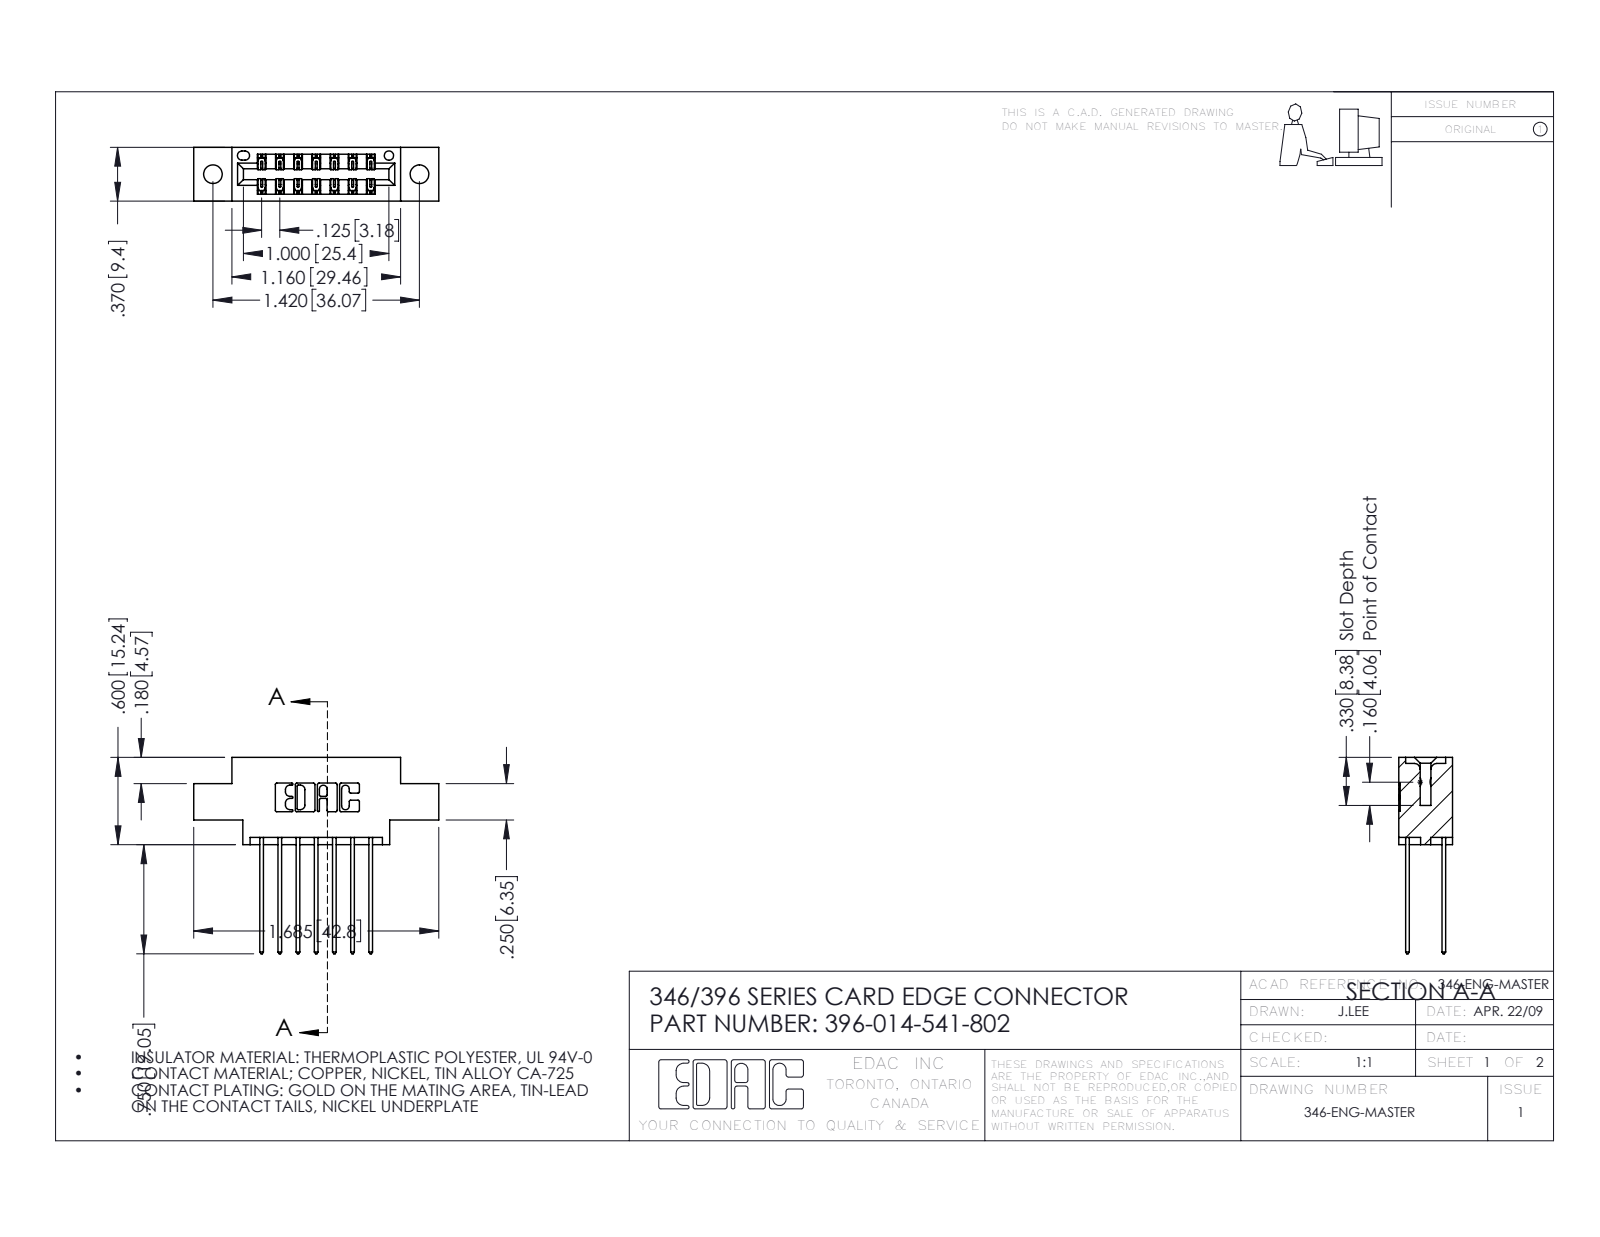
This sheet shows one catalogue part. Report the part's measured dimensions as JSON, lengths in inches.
{"part_name": "396-014-541-802; 345-292-001_345-293-141; 346 Part_0.170 Offset - 0.128 Dia", "step_written_by": "SolidWorks 2016 (CONFIG_CONTROL_DESIGN)", "units": "inches", "bodies": {"solids": 15, "faces": 854, "planar": 570, "cylindrical": 284, "other": 0}, "overall_size": [1.685, 1.35, 0.37], "volume_in3": 0.231, "surface_area_in2": 7.682, "round_holes": [[0.128, 2], [0.064, 1]], "partial_cylinders_radius": [[0.01, 22], [0.006, 21], [0.01, 14], [0.007, 6], [0.031, 6], [0.026, 3], [0.014, 2], [0.022, 2]], "face_to_face_distances": [0.25, 0.048, 0.322, 0.37, 0.072, 0.298, 0.025, 0.275, 0.225, 0.148], "hole_center_spacings": [0.246, 1.217, 1.42]}
